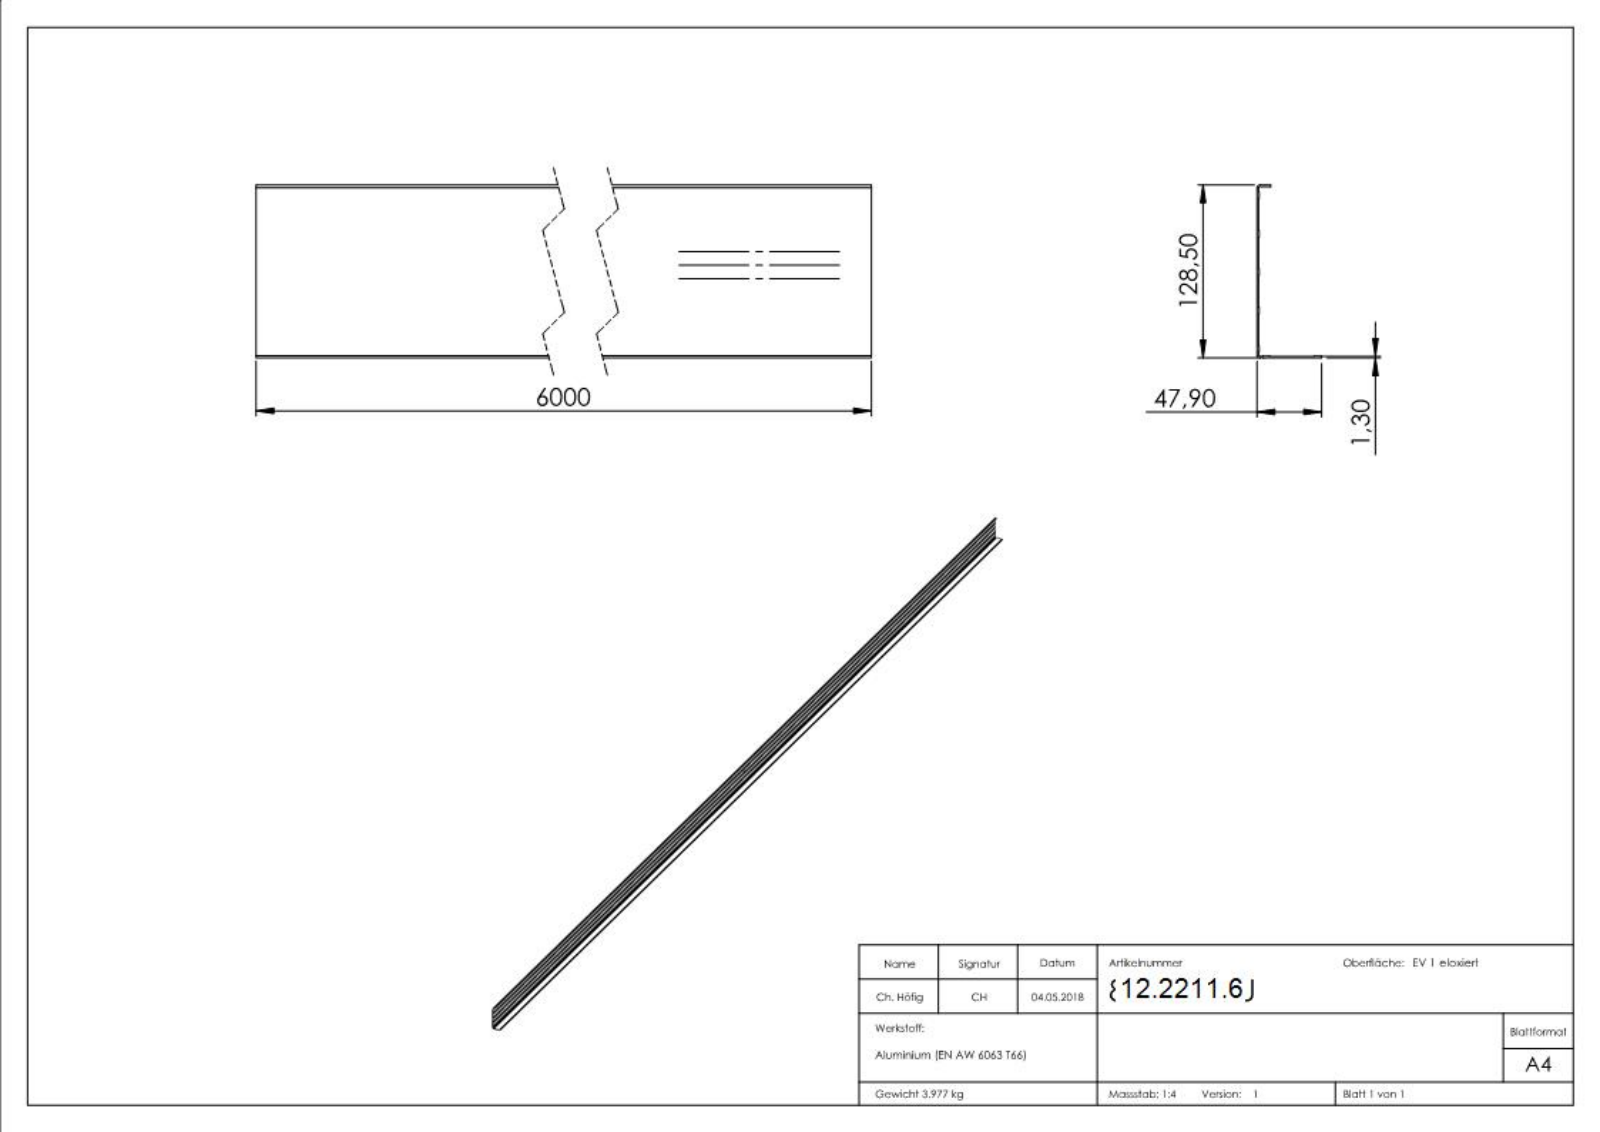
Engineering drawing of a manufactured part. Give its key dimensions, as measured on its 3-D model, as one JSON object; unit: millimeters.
{"part_name": "80610-ALU", "step_written_by": "SolidWorks 2015 (CONFIG_CONTROL_DESIGN)", "units": "millimeters", "bodies": {"solids": 1, "faces": 259, "planar": 153, "cylindrical": 7, "other": 99}, "overall_size": [6000, 128.5, 47.9], "volume_mm3": 1473000, "surface_area_mm2": 2227000, "partial_cylinders_radius": [[0.3, 2], [1.2, 2], [1.7, 1], [2, 1], [2.2, 1]], "face_to_face_distances": [1.3, 1.5, 128.5, 127.2, 127, 10.2, 28.5, 8.9, 8.7, 47.9]}
